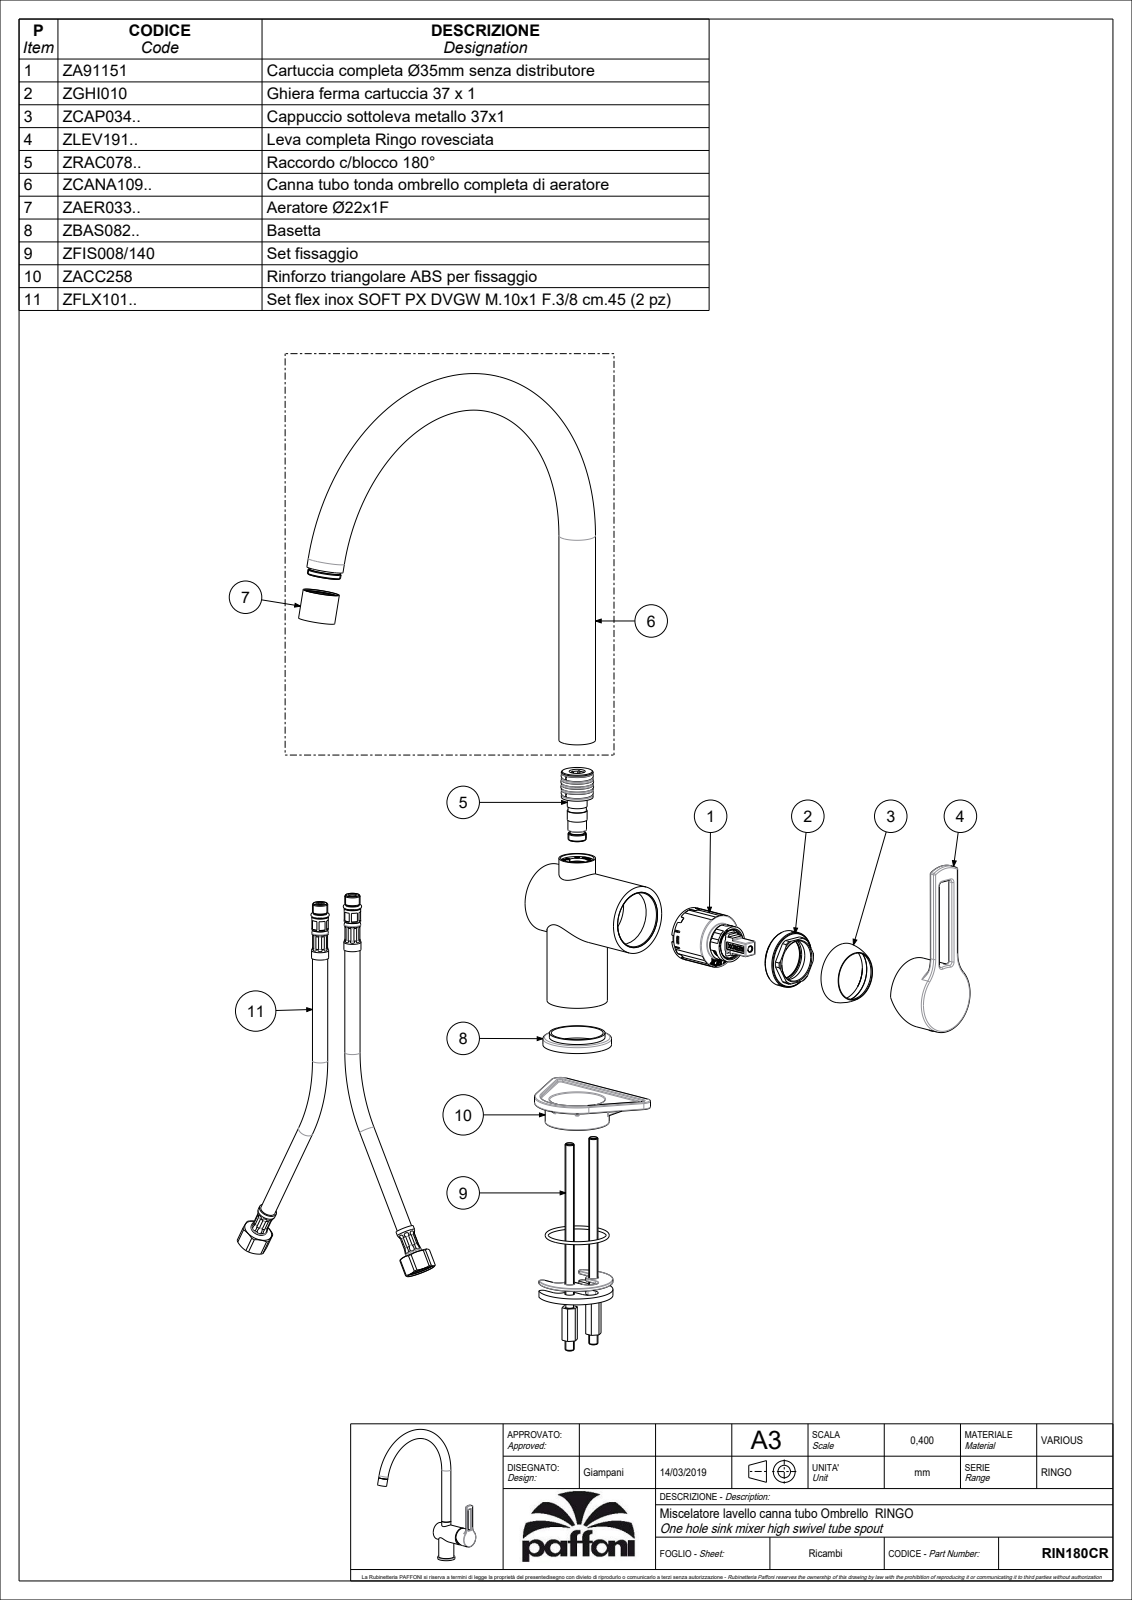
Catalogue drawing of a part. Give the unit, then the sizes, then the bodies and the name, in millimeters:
Units: millimetres
Overall size (bounding box): 370.79 × 272.5 × 113.63
Round holes (diameter × count): ⌀2.5 ×9, ⌀5.5 ×3, ⌀6 ×3, ⌀11 ×3, ⌀7 ×2, ⌀9 ×2, ⌀36 ×2, ⌀3 ×1, ⌀3.4 ×1, ⌀3.5 ×1, ⌀4 ×1, ⌀4.6 ×1
Round bosses / shafts (diameter × count): ⌀24 ×2, ⌀19.5 ×2, ⌀4 ×2, ⌀45 ×1, ⌀44.8 ×1, ⌀44.7 ×1, ⌀39.6 ×1, ⌀38.5 ×1
Partial cylindrical surfaces — rounded edges, fillets, slot ends (radius × count): R0.5 ×60, R0.3 ×20, R0.2 ×16, R1 ×14, R24.3 ×12, R1.7 ×6, R2 ×6, R1.5 ×5
Main face-to-face distances: 3.5, 1.5, 5, 2, 70.8, 0.5, 6.5, 11.5, 4.5, 6
Hole centre spacings: 8.9, 4.61, 17.65, 5.06, 8.49, 9.43, 9.6, 10.59
Volume: 196 035 mm³ · Surface area: 150 639 mm²
Bodies: 3 solids, 3614 faces (2531 planar, 577 cylindrical, 506 other)
Part name (STEP PRODUCT): RIN180CR
STEP written by: CREO PARAMETRIC BY PTC INC, 2020044 (CONFIG_CONTROL_DESIGN)
